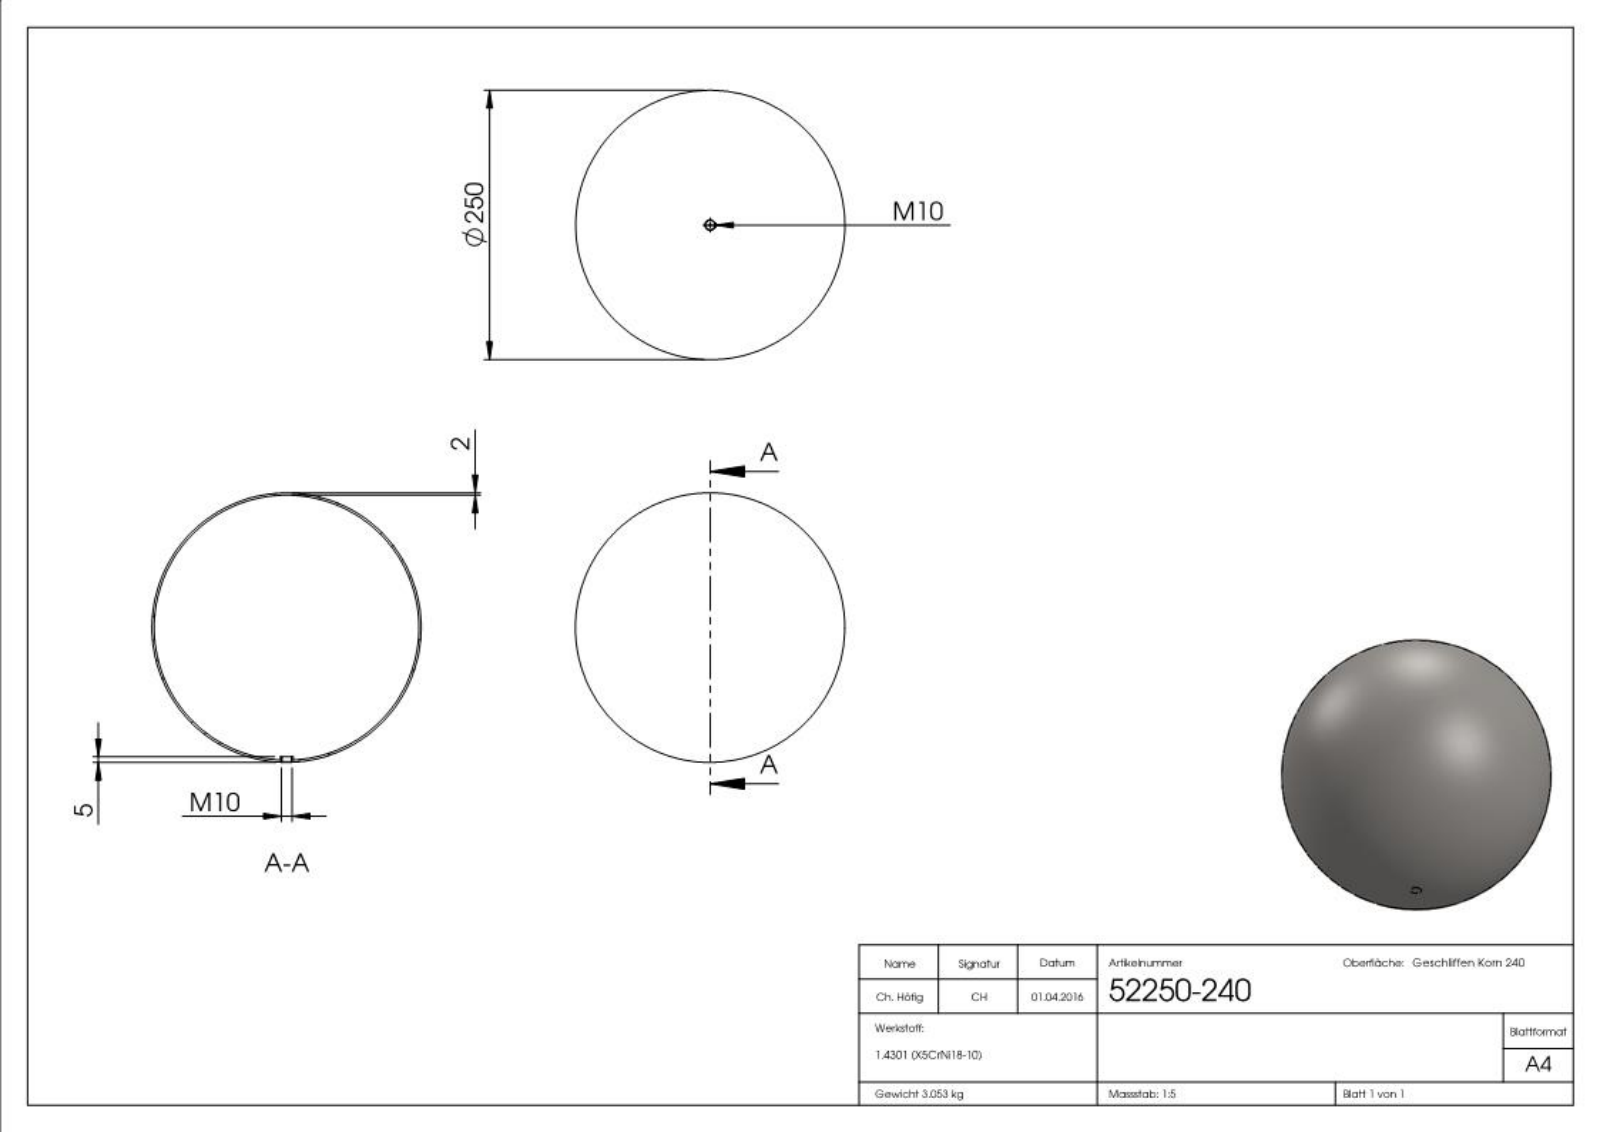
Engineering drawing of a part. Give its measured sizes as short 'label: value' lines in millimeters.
name: 52250-240
written by: SolidWorks 2015 (CONFIG_CONTROL_DESIGN)
unit: mm
bodies: 1 solid, 235 faces (102 planar, 4 cylindrical, 129 other)
size: 250 × 250 × 249.91
volume: 386 501 mm³; area: 386 593 mm²
holes: 1× ⌀8.5
bosses: 1× ⌀12
